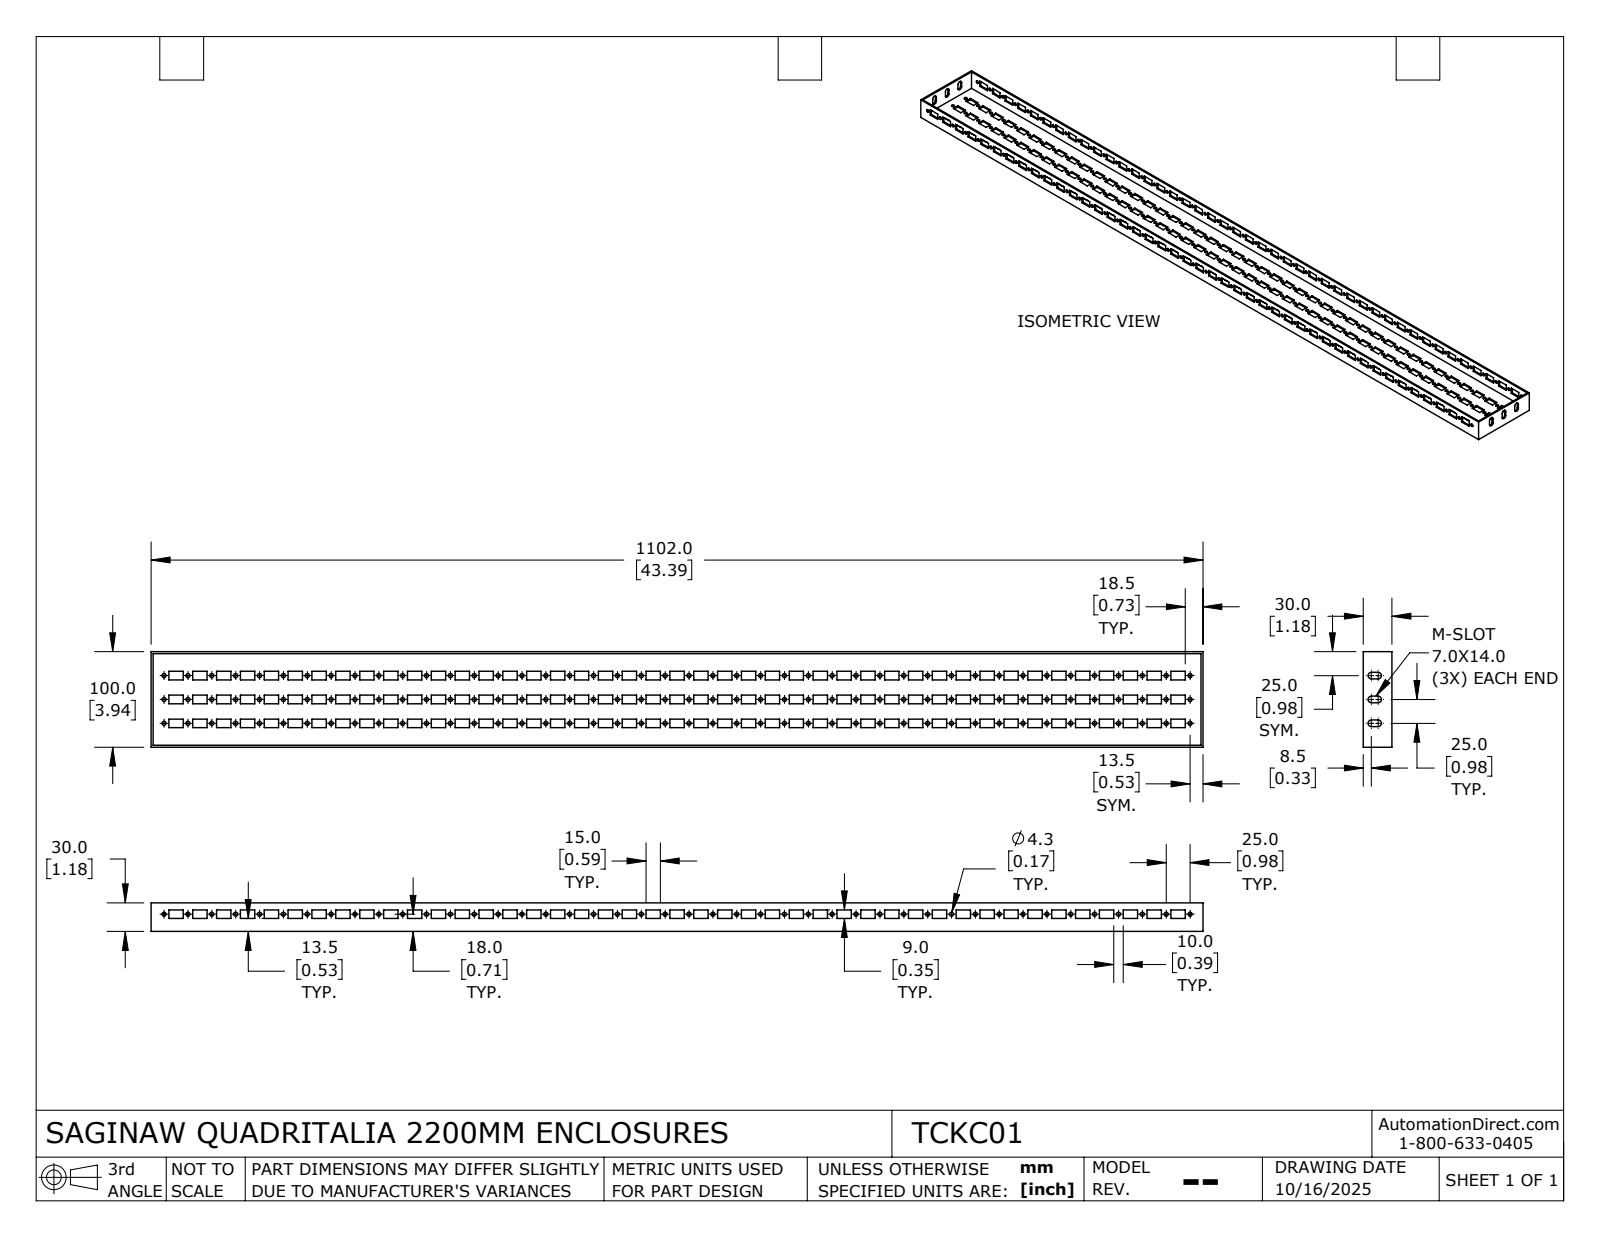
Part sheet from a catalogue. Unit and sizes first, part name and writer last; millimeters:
Units: millimetres
Overall size (bounding box): 1102 × 100 × 30
Round holes (diameter × count): ⌀4.25 ×176
Partial cylindrical surfaces — rounded edges, fillets, slot ends (radius × count): R3.5 ×6
Main face-to-face distances: 2, 98, 100, 96, 25, 9, 20.5, 1100, 30, 28
Hole centre spacings: 25, 50, 55.9, 75, 100, 125, 35.36, 150
Volume: 289 234 mm³ · Surface area: 320 989 mm²
Bodies: 1 solid, 1115 faces (883 planar, 232 cylindrical, 0 other)
Part name (STEP PRODUCT): TCKC01
STEP written by: SolidWorks 2024 (AUTOMOTIVE_DESIGN)
